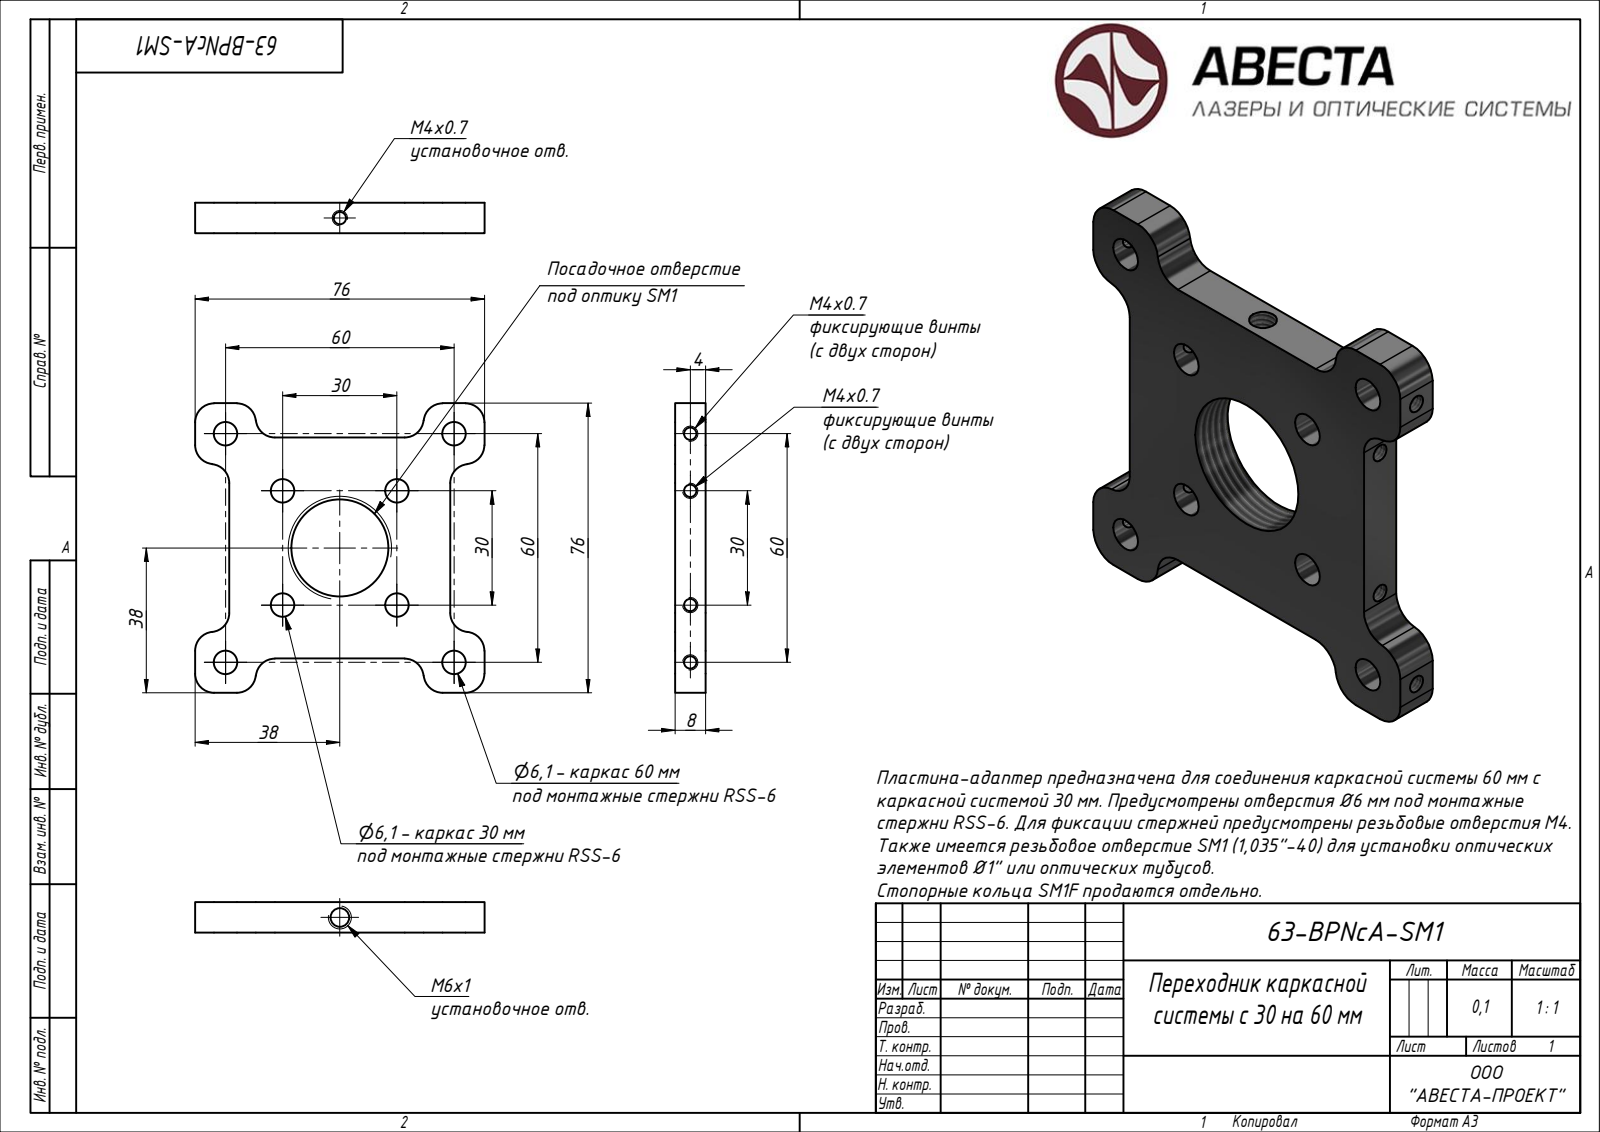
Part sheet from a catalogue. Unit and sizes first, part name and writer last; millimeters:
Units: millimetres
Overall size (bounding box): 76 × 76 × 8
Round holes (diameter × count): ⌀6.1 ×8, ⌀3.24 ×5, ⌀4.92 ×1, ⌀25.48 ×1
Partial cylindrical surfaces — rounded edges, fillets, slot ends (radius × count): R5 ×20
Main face-to-face distances: 8, 58, 9, 67, 76
Hole centre spacings: 21.21, 47.43, 42.43, 30, 60, 63.64, 15, 45
Volume: 26 692 mm³ · Surface area: 12 075 mm²
Bodies: 1 solid, 55 faces (14 planar, 39 cylindrical, 2 other)
Part name (STEP PRODUCT): 63-BPNcA-SM1
STEP written by: Autodesk Inventor 2020 (AUTOMOTIVE_DESIGN)
